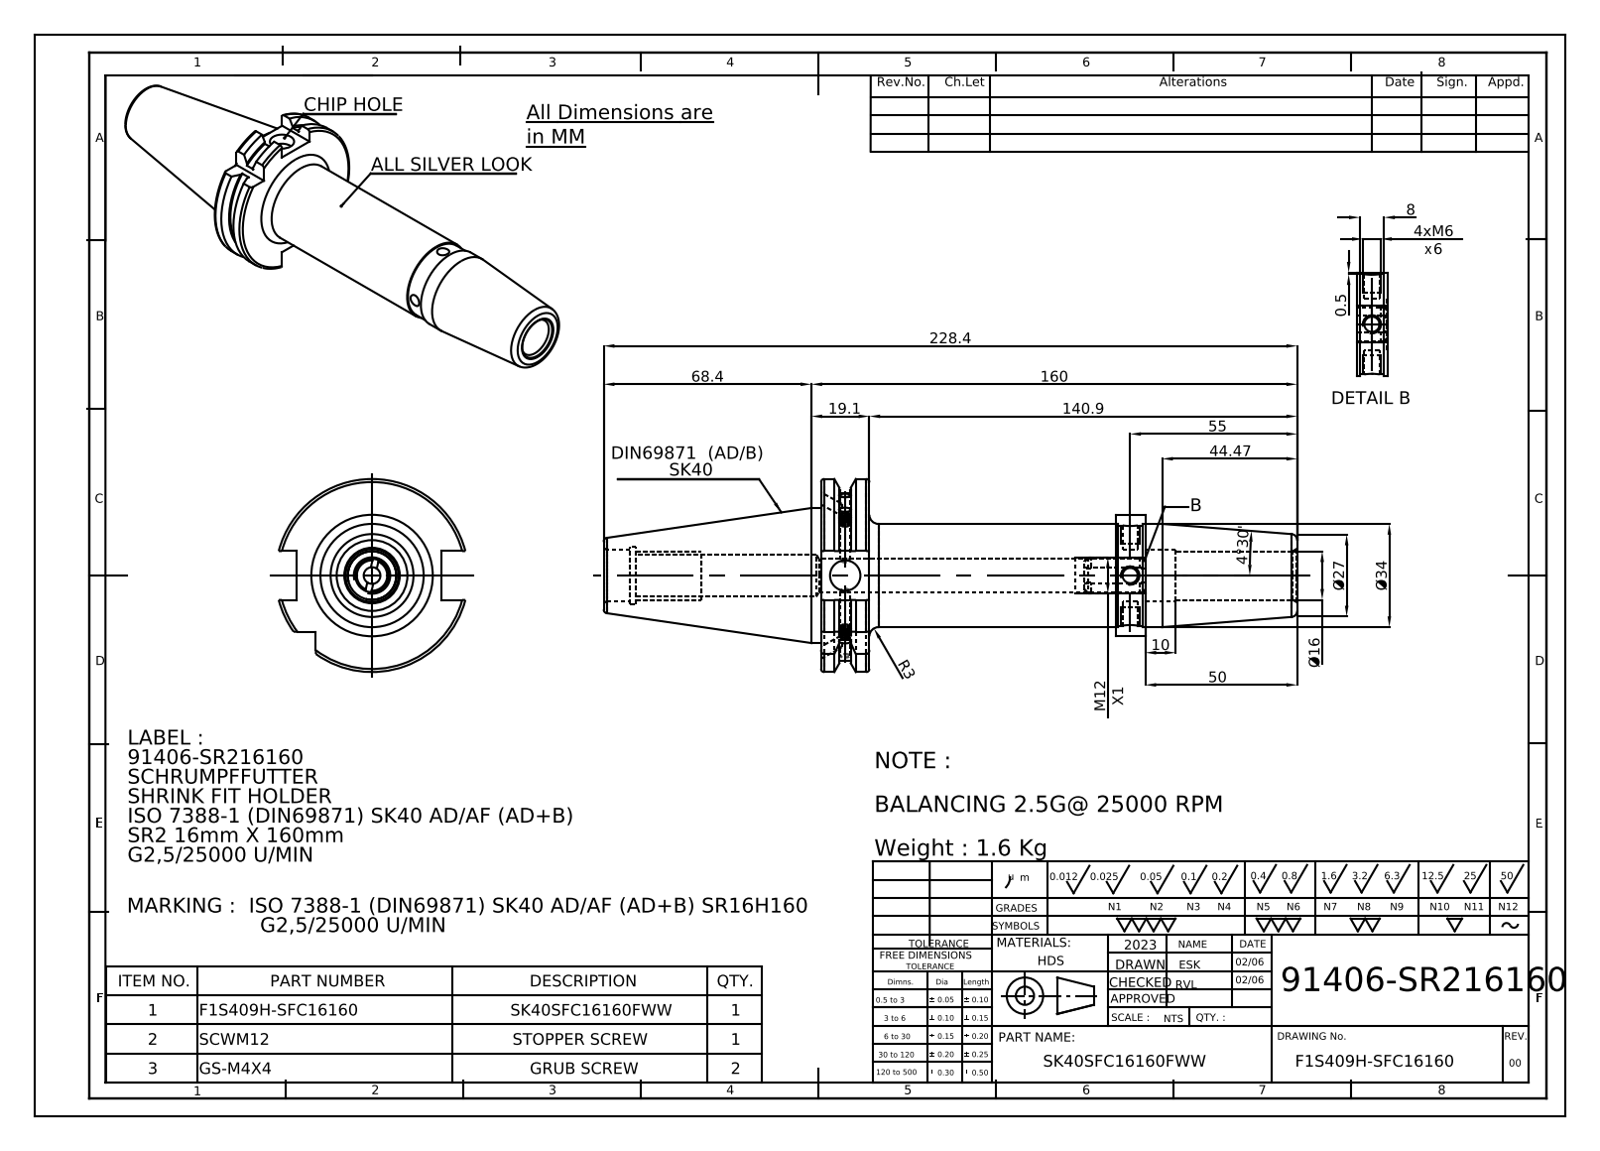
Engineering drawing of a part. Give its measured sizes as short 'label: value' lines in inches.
name: SK40SFC16160FWW; GS-M4X4_DIN 913 - M4 x 4-N; 91406-SR216160; SCWM12
written by: SolidWorks 2018 (CONFIG_CONTROL_DESIGN)
unit: in
bodies: 4 solids, 238 faces (70 planar, 70 cylindrical, 98 other)
size: 8.992 × 2.502 × 2.42
volume: 12.29 in³; area: 66.64 in²
holes: 2× ⌀0.197, 1× ⌀0.13, 1× ⌀0.217, 1× ⌀0.394, 1× ⌀0.433, 1× ⌀0.551, 1× ⌀0.63, 1× ⌀0.669, 1× ⌀0.669, 1× ⌀0.748
bosses: 2× ⌀0.157, 1× ⌀1.75, 1× ⌀1.339, 1× ⌀1.299, 1× ⌀0.472
rounds: 1× R1.107, 1× R1.251
face distances: 0.626, 0.634, 1.882, 4.205, 3.579, 6.173, 5.547, 1.969, 6.602, 2.819
hole spacings: 3.695
